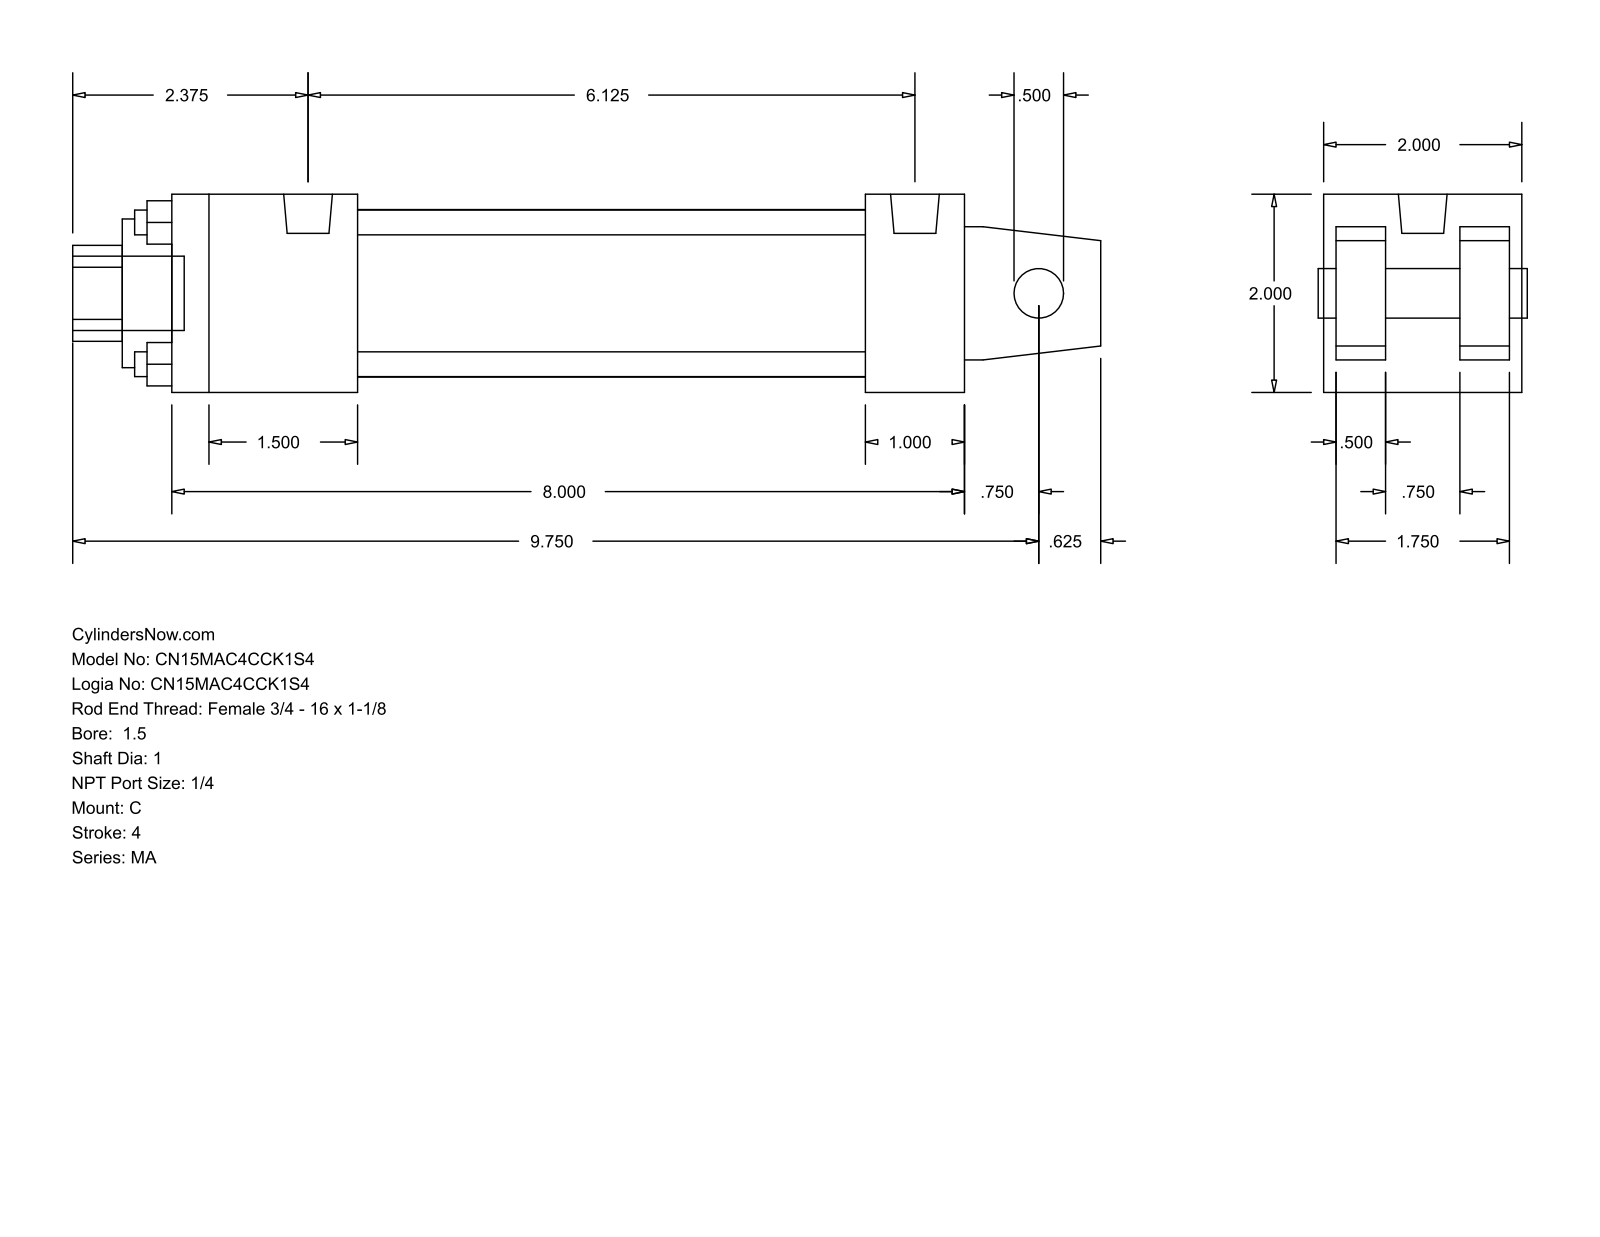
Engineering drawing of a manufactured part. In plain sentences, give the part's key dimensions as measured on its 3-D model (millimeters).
The part is named "MA_C__0150_1". Its 3-D file was written by "GSSL Pune (CONFIG_CONTROL_DESIGN)". It is 0 solids with 103 faces: 76 planar, 27 cylindrical and 0 other. Overall it measures 263.52 by 50.8 by 50.8 millimeters. Round holes: 4 of diameter 6.35, 1 of diameter 12.7, 1 of diameter 25.4, 1 of diameter 38.1, 1 of diameter 42.93. Round bosses or shafts: 4 of diameter 7.94, 2 of diameter 12.49, 1 of diameter 19.05. Partial cylindrical surfaces (rounded edges, fillets, slot ends): 1 of radius 12.29. The main face-to-face distances are 50.8, 47.63, 12.7, 3.17, 15.87, 34.93, 31.76, 44.46, 203.2, 25.4. The hole center spacings are 25.68, 36.32, 51.36.
